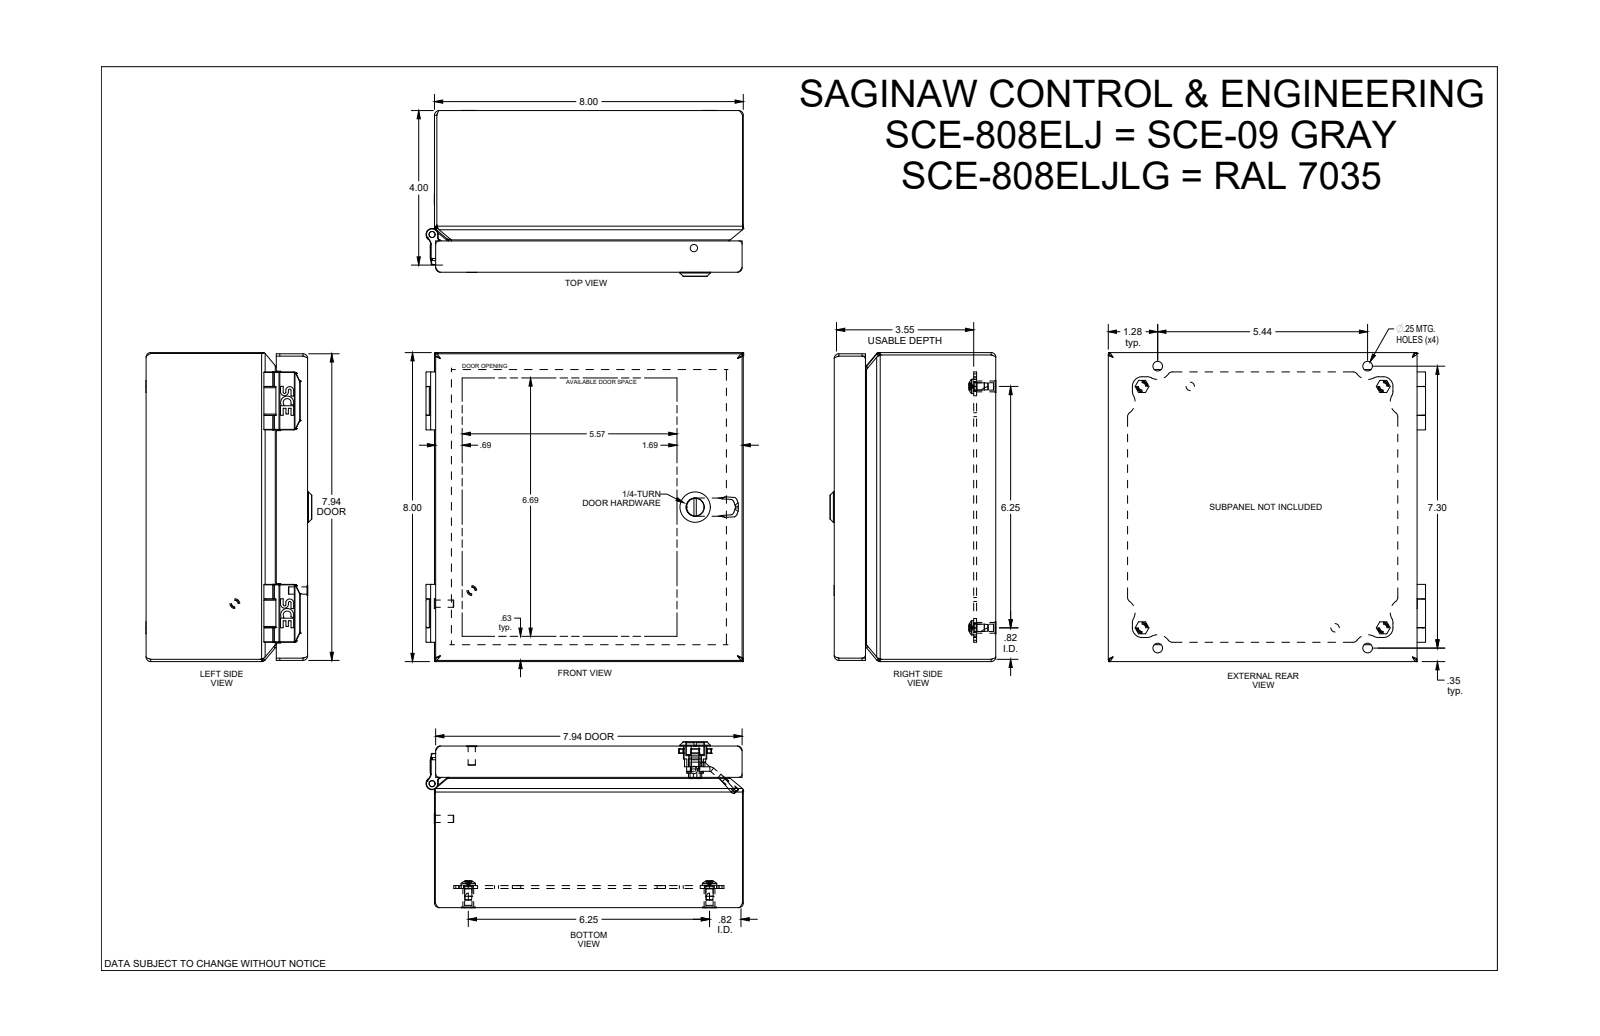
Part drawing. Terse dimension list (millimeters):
name: SCE-808ELJ
written by: SolidWorks 2021 (AUTOMOTIVE_DESIGN)
unit: mm
bodies: 22 solids, 1278 faces (397 planar, 378 cylindrical, 503 other)
size: 208.8 × 203.2 × 109
volume: 340 500 mm³; area: 435 100 mm²
holes: 4× ⌀6.4, 4× ⌀7.2, 2× ⌀4.3, 2× ⌀5.5, 1× ⌀4, 1× ⌀5.1, 1× ⌀6.1, 1× ⌀6.5, 1× ⌀6.8, 1× ⌀7.2, 1× ⌀8.3, 1× ⌀12.1
bosses: 5× ⌀4.8, 4× ⌀9.5, 2× ⌀12.2, 2× ⌀6.6, 2× ⌀2.5, 2× ⌀0.5, 1× ⌀20, 1× ⌀13.9
rounds: 66× R2.7, 36× R0.1, 32× R0.2, 21× R0.3, 16× R1.3, 12× R0.6, 12× R6.4, 10× R0.3
face distances: 1.5, 201.7, 1.5, 104.8, 103.3, 106.3, 104.8, 14.5, 13, 90.3
hole spacings: 158.8, 31.8, 127, 80, 158.8, 161.9, 169.1, 203.3
